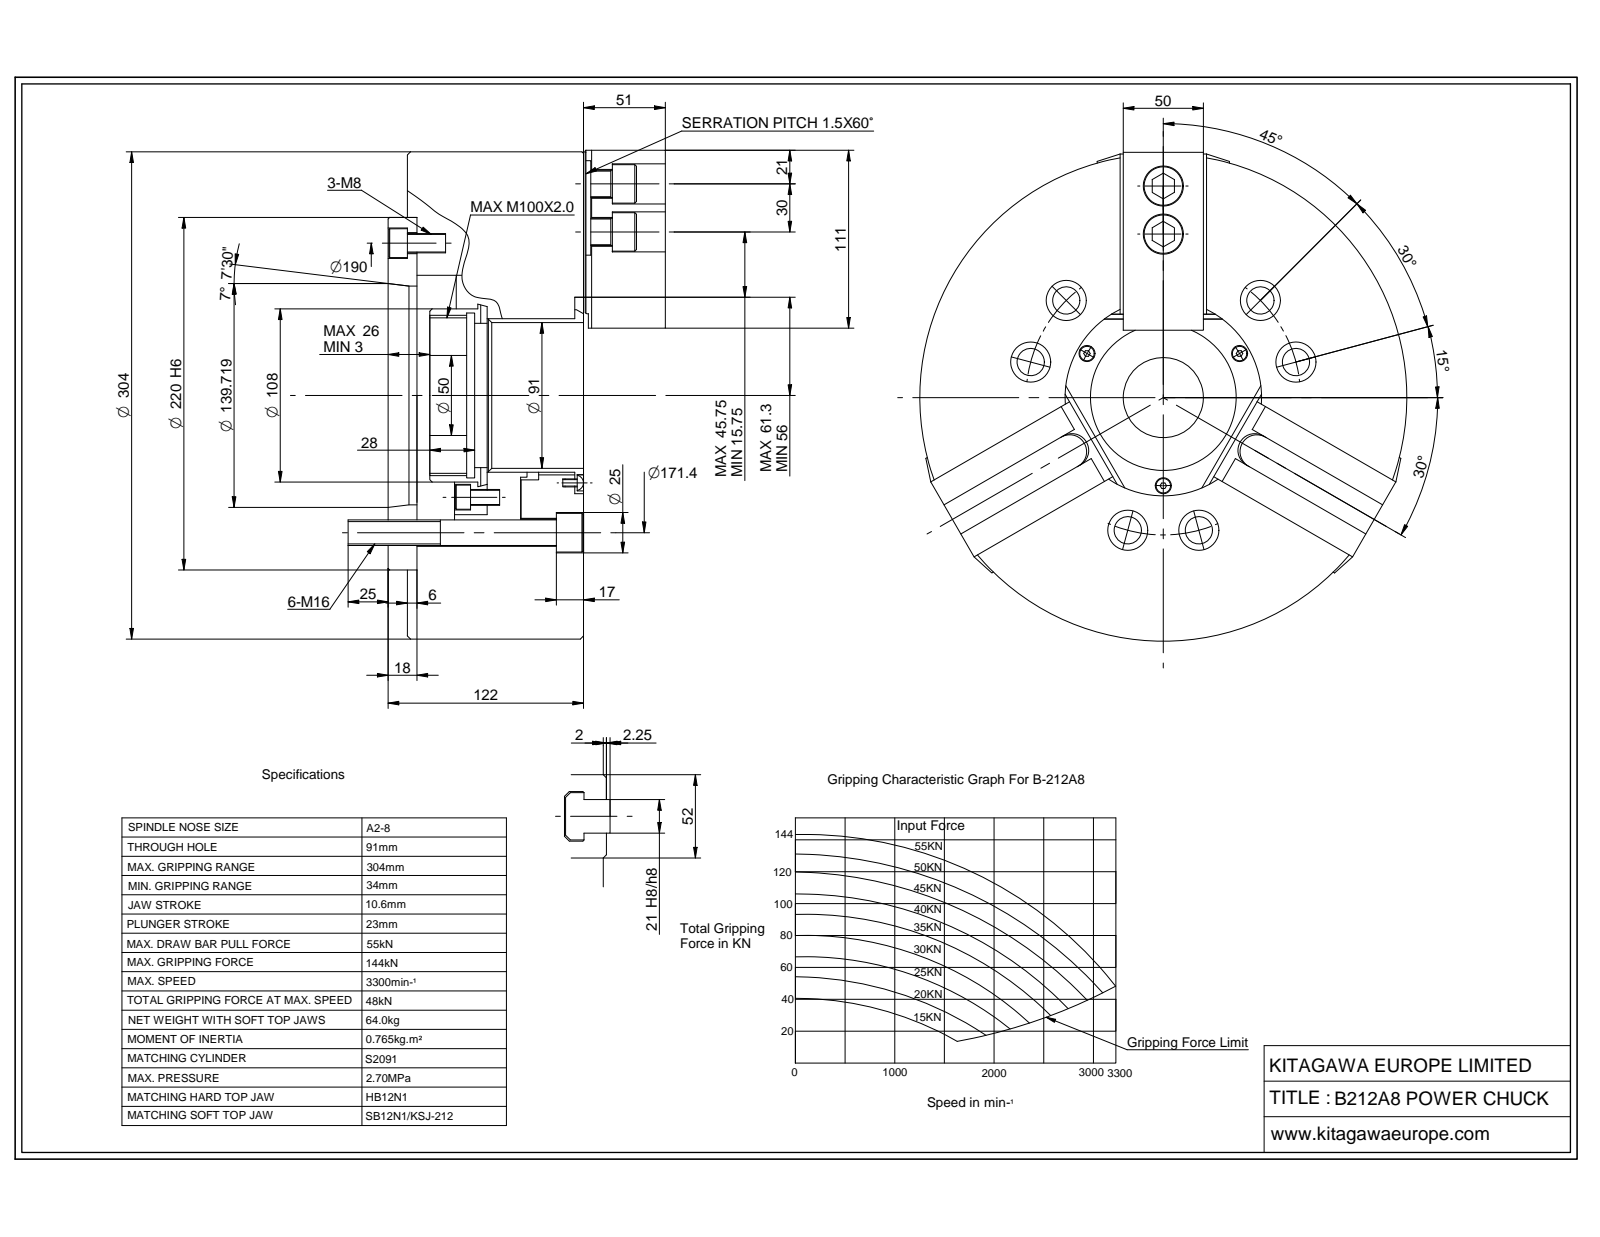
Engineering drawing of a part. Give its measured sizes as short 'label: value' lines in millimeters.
name: cb10a08
written by: Unknown (AUTOMOTIVE_DESIGN)
unit: mm
bodies: 1 solid, 4323 faces (3527 planar, 372 cylindrical, 424 other)
size: 304 × 304 × 178.2
volume: 7 681 000 mm³; area: 727 603 mm²
holes: 18× ⌀17, 15× ⌀14, 15× ⌀25, 9× ⌀3.8, 9× ⌀11, 7× ⌀6, 6× ⌀8.38, 6× ⌀10, 6× ⌀16, 4× ⌀4.92, 3× ⌀1.5, 3× ⌀1.9
bosses: 12× ⌀24, 12× ⌀16, 3× ⌀10.5, 1× ⌀304
rounds: 12× R0.4, 12× R0.45, 12× R0.6, 12× R5, 12× R10, 6× R0.8, 6× R1.4, 6× R6.5
face distances: 110, 12, 122, 35.5, 50, 36.5, 62.5, 18, 173.2, 161.2
hole spacings: 31.01, 31.06, 43.66, 85.73, 96.04, 105.75, 114.57, 123.87
